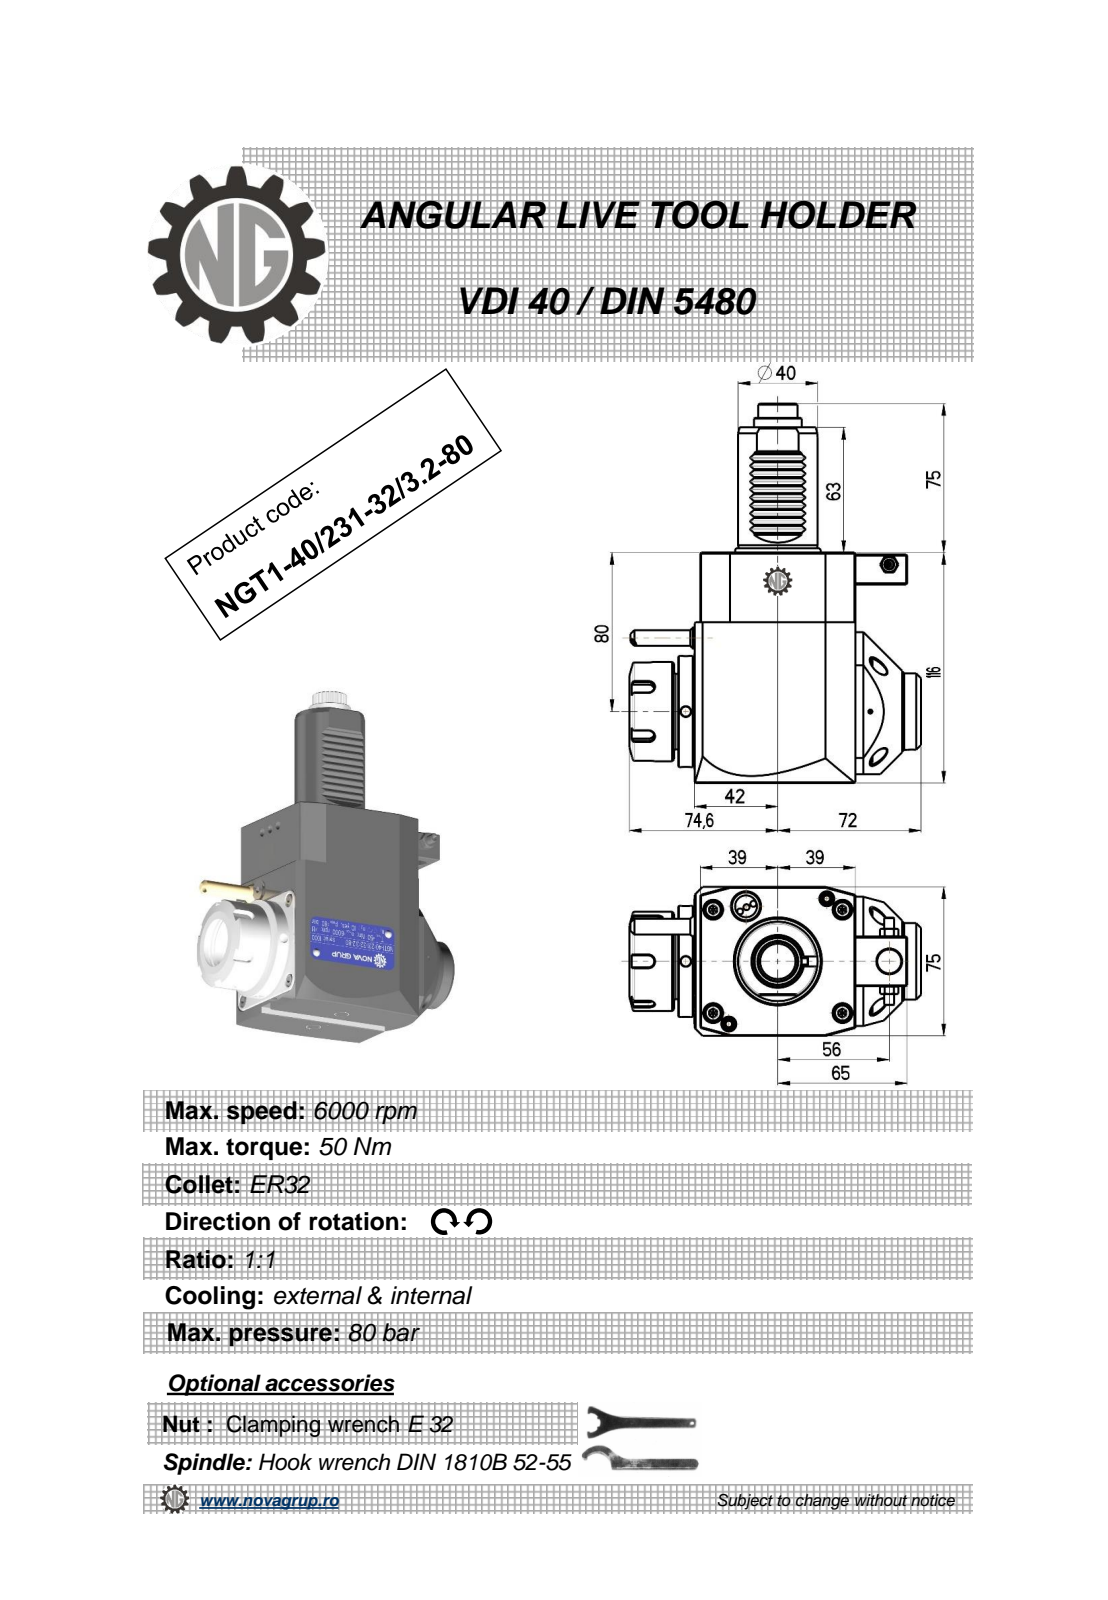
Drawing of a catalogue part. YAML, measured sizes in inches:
part_name: "NGT1_40_231_32_3_2_80"
step_written_by: "PRO/ENGINEER BY PARAMETRIC TECHNOLOGY CORPORATION, 2010280 (CONFIG_CONTROL_DESIGN)"
units: inches
bodies: {solids: 1, faces: 537, planar: 193, cylindrical: 183, other: 161}
overall_size: [7.52, 5.772, 2.953]
volume: 55.75
surface_area: 113.3
round_holes:
  - {diameter: 0.197, count: 3}
  - {diameter: 0.118, count: 1}
  - {diameter: 0.165, count: 1}
  - {diameter: 0.374, count: 1}
  - {diameter: 0.472, count: 1}
  - {diameter: 1.063, count: 1}
round_bosses_or_shafts:
  - {diameter: 2.205, count: 1}
  - {diameter: 1.969, count: 1}
  - {diameter: 1.693, count: 1}
  - {diameter: 1.575, count: 1}
  - {diameter: 1.516, count: 1}
  - {diameter: 0.945, count: 1}
  - {diameter: 0.441, count: 1}
  - {diameter: 0.353, count: 1}
partial_cylinders:
  - {radius: 0.082, count: 48}
  - {radius: 0.01, count: 12}
  - {radius: 0.012, count: 10}
  - {radius: 0.009, count: 6}
  - {radius: 0.118, count: 5}
  - {radius: 0.357, count: 1}
  - {radius: 0.391, count: 1}
  - {radius: 0.591, count: 1}
face_to_face_distances: [2.953, 4.567, 3.189, 3.071, 0.118, 0.295, 0.11, 3.181, 0.02, 4.37]
hole_center_spacings: [1.523, 1.611, 2.815, 4.026, 4.969]
